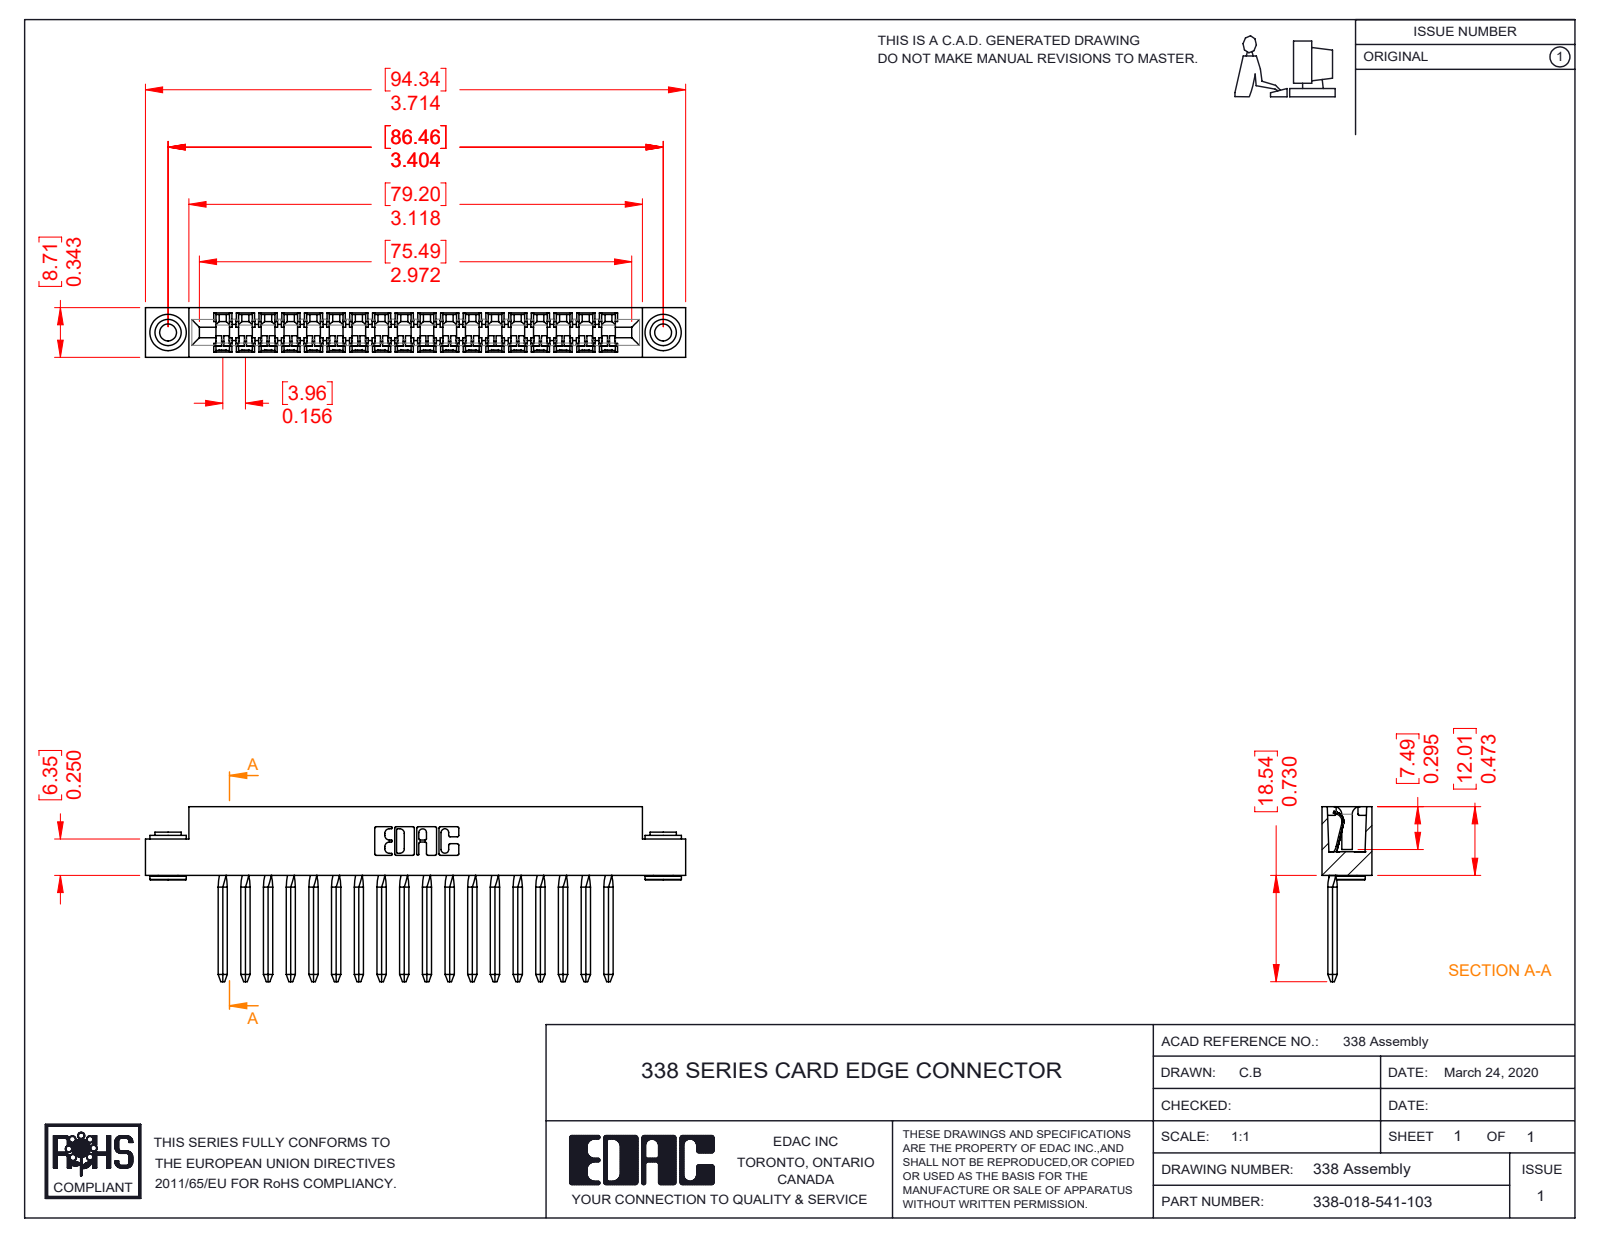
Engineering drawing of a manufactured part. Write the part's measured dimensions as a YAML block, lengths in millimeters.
part_name: "345-250-002_345-250-002-102; 338-290-001_541; 338-018-541-103; 338-210-001_338-210-018-004"
step_written_by: "SolidWorks 2016 (CONFIG_CONTROL_DESIGN)"
units: millimeters
bodies: {solids: 21, faces: 1820, planar: 1244, cylindrical: 496, other: 80}
overall_size: [94.3, 30.6, 8.7]
volume: 6590
surface_area: 10680
round_holes:
  - {diameter: 2.9, count: 2}
  - {diameter: 4, count: 2}
round_bosses_or_shafts:
  - {diameter: 6.4, count: 2}
  - {diameter: 4.6, count: 2}
  - {diameter: 3.5, count: 2}
partial_cylinders:
  - {radius: 0.6, count: 74}
  - {radius: 0.3, count: 22}
  - {radius: 0.2, count: 18}
  - {radius: 1.4, count: 15}
  - {radius: 1.7, count: 15}
  - {radius: 2.5, count: 14}
  - {radius: 0.2, count: 6}
  - {radius: 0.8, count: 6}
face_to_face_distances: [8.7, 4, 15.8, 2.8, 19.8, 11.9, 5.3, 3.4, 5.6, 7.9]
hole_center_spacings: [86.5]
